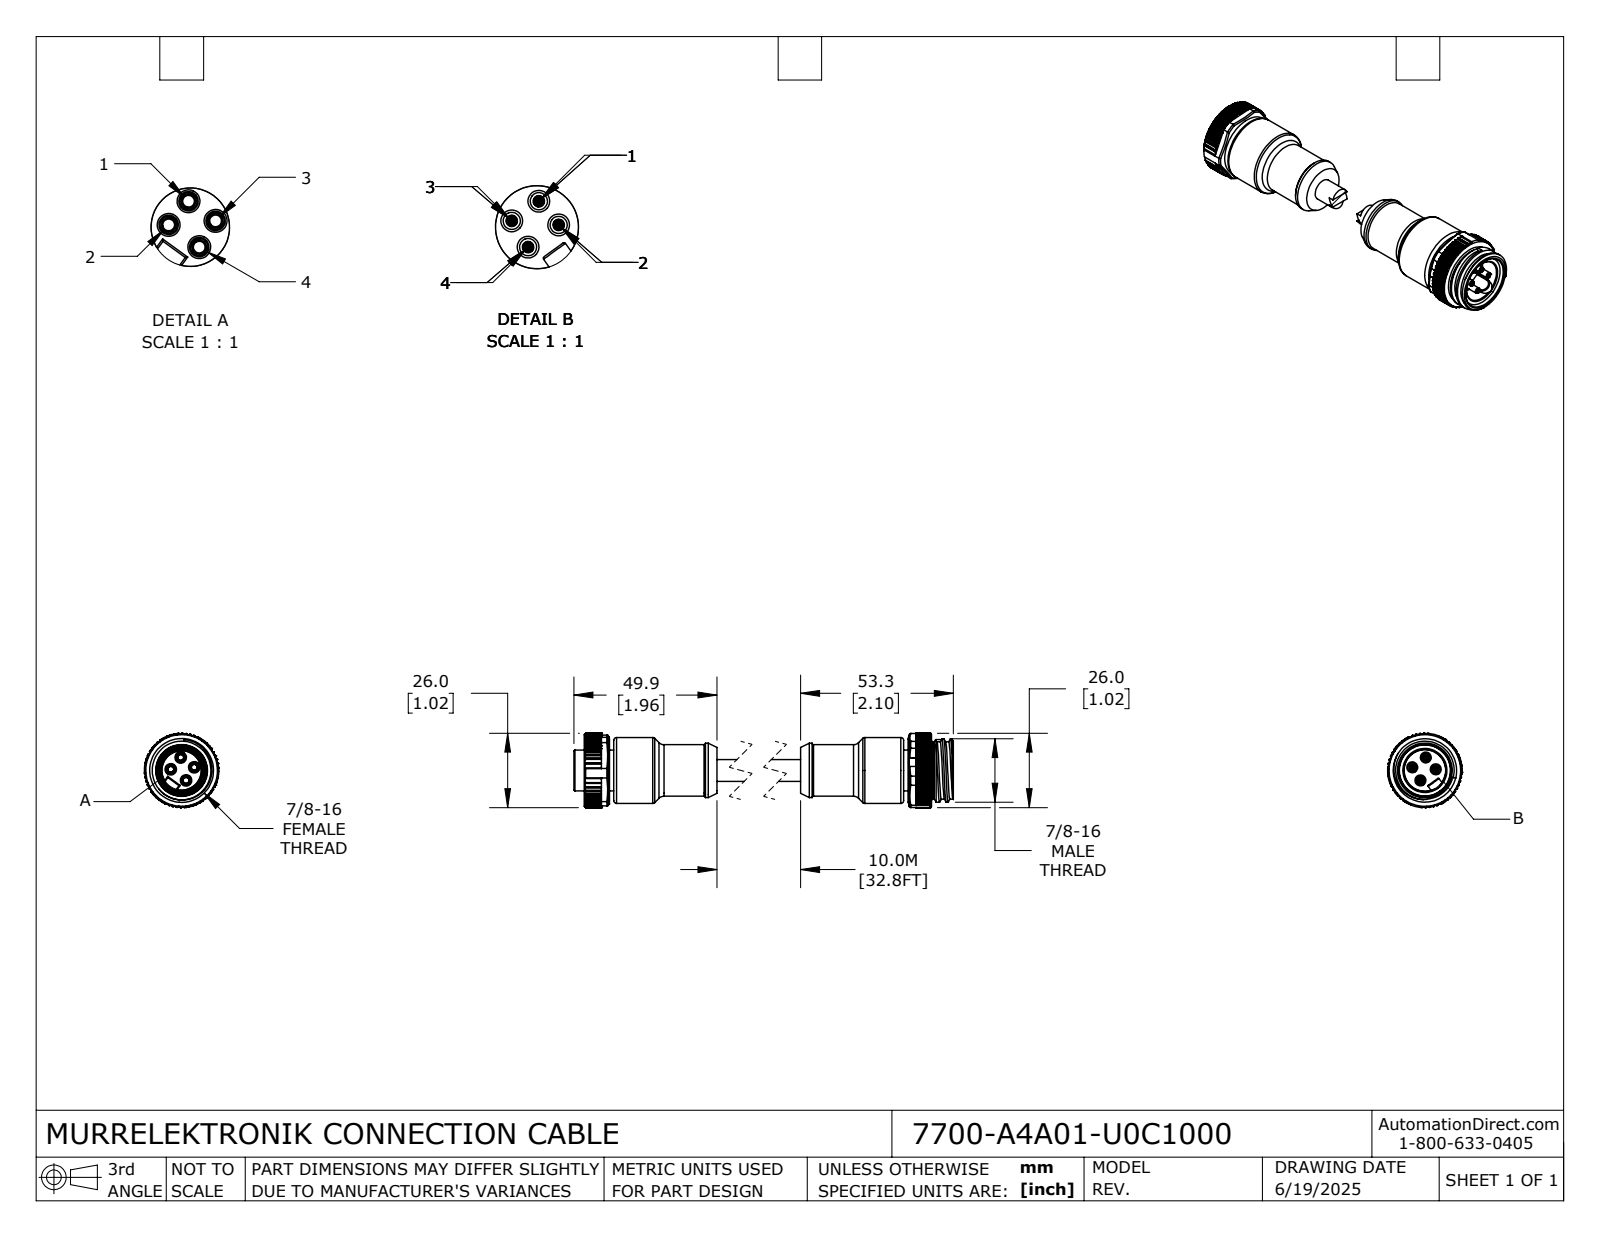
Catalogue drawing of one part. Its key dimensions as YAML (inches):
part_name: "7700-A4A01-U0C1000_FEMALE; 7700-A4A01-U0C1000_MALE; 7700-A4A01-U0C1000"
step_written_by: "SolidWorks 2024 (CONFIG_CONTROL_DESIGN)"
units: inches
bodies: {solids: 2, faces: 1226, planar: 520, cylindrical: 543, other: 163}
overall_size: [5.244, 1.024, 1.024]
volume: 2.059
surface_area: 22.09
round_holes:
  - {diameter: 0.081, count: 4}
  - {diameter: 0.118, count: 4}
  - {diameter: 0.134, count: 4}
  - {diameter: 0.61, count: 1}
  - {diameter: 0.614, count: 1}
  - {diameter: 0.728, count: 1}
  - {diameter: 0.807, count: 1}
  - {diameter: 0.875, count: 1}
round_bosses_or_shafts:
  - {diameter: 0.079, count: 4}
  - {diameter: 0.906, count: 1}
  - {diameter: 0.873, count: 1}
  - {diameter: 0.789, count: 1}
  - {diameter: 0.787, count: 1}
  - {diameter: 0.748, count: 1}
  - {diameter: 0.713, count: 1}
  - {diameter: 0.709, count: 1}
partial_cylinders:
  - {radius: 0.008, count: 252}
  - {radius: 0.012, count: 18}
  - {radius: 0.004, count: 8}
  - {radius: 0.027, count: 4}
  - {radius: 0.029, count: 4}
  - {radius: 0.093, count: 1}
  - {radius: 0.512, count: 1}
face_to_face_distances: [0.059, 4.075, 1.476, 2.657, 1.417, 2.598, 4.134, 0.346, 4.421, 0.287]
hole_center_spacings: [0.15, 0.324, 0.179, 0.179, 0.212, 0.213, 0.23, 0.26]
